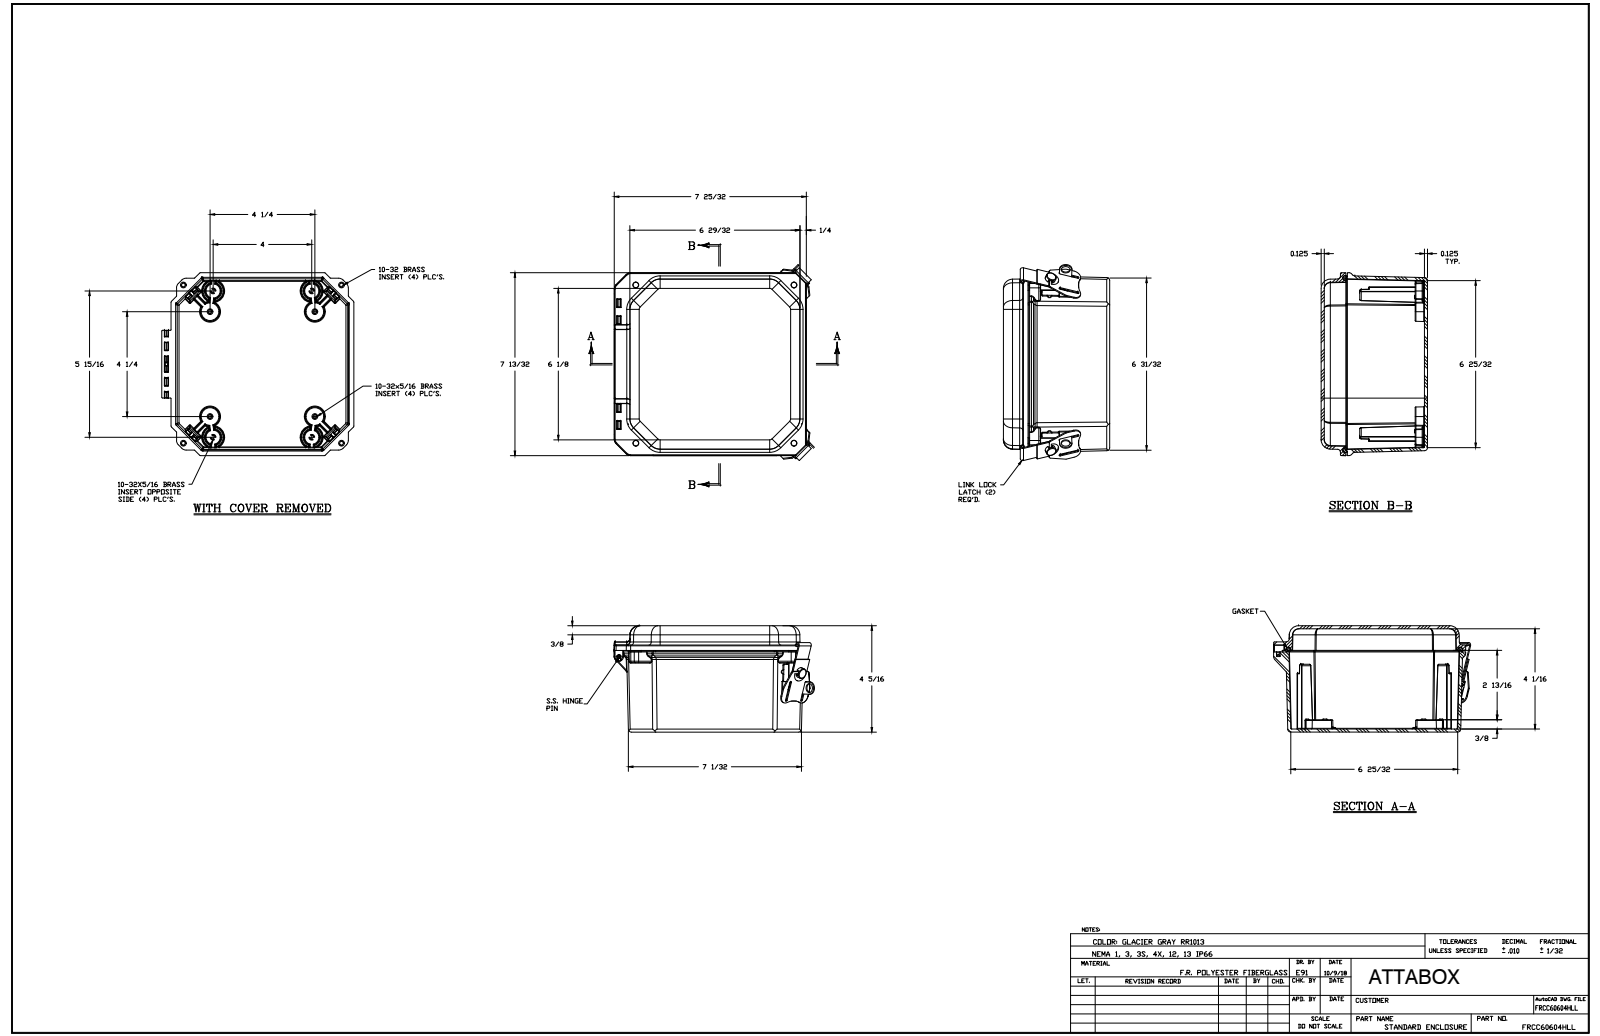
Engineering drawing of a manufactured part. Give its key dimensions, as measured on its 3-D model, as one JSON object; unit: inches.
{"part_name": "FRCC60604HLL", "step_written_by": "SolidWorks 2018 (AUTOMOTIVE_DESIGN)", "units": "inches", "bodies": {"solids": 35, "faces": 2191, "planar": 648, "cylindrical": 845, "other": 698}, "overall_size": [8.262, 8.214, 4.312], "volume_in3": 32.59, "surface_area_in2": 512.2, "round_holes": [[0.156, 12], [0.152, 8], [0.15, 4], [0.219, 4], [0.252, 4], [0.312, 4], [0.05, 2], [0.098, 2], [0.12, 2], [0.363, 2], [0.137, 1]], "round_bosses_or_shafts": [[0.246, 12], [0.87, 4], [0.209, 4], [0.135, 3], [0.6, 2], [0.2, 2], [0.05, 2], [0.135, 1]], "partial_cylinders_radius": [[0.01, 156], [0.005, 96], [0.02, 65], [0.125, 41], [0.03, 38], [0.039, 28], [0.25, 26], [0.03, 24]], "face_to_face_distances": [0.125, 4.187, 4.062, 4.312, 0.124, 0.125, 3.531, 0.656, 0.375, 3.406], "hole_center_spacings": [5.441, 6.414, 6.289, 4.25, 5.091, 7.541, 0.849, 1.231]}
